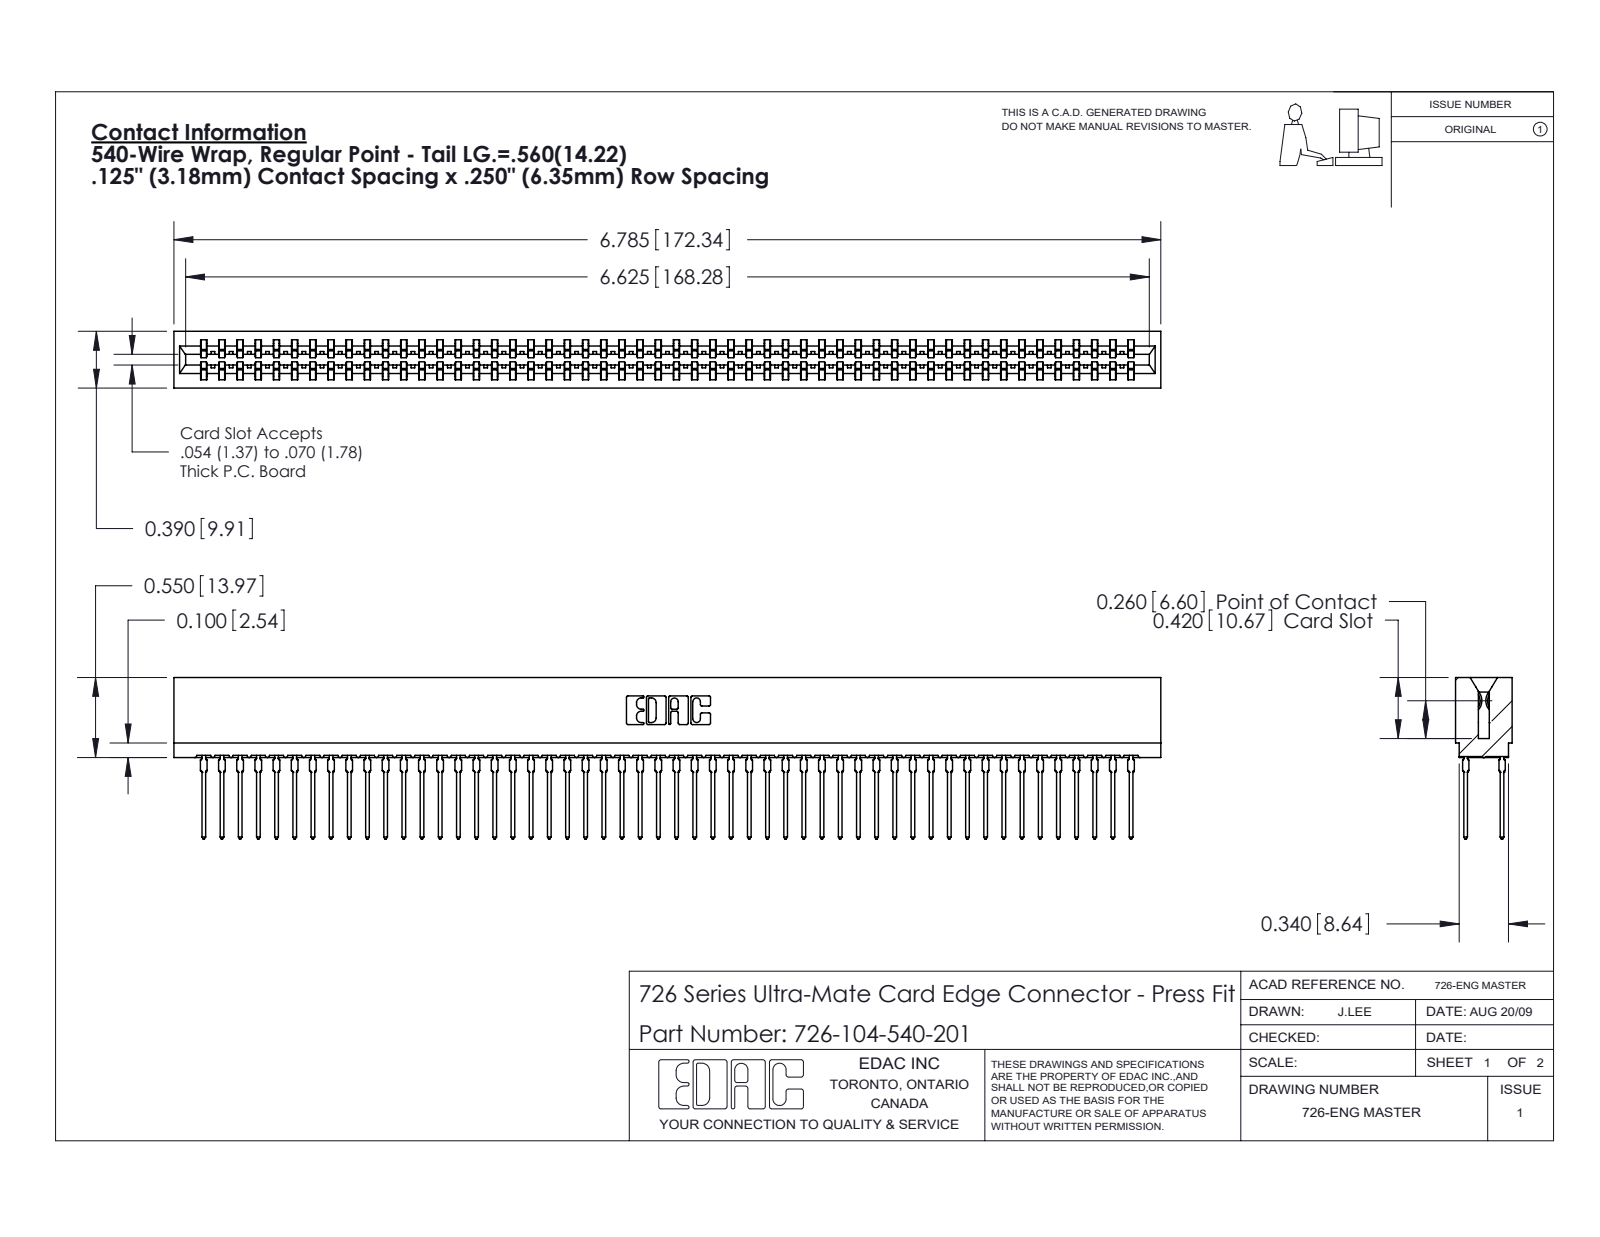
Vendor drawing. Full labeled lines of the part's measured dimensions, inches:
Part name (STEP PRODUCT): 726-104-540-201; 746-292-001_540; 726 Part_.515 Slot Depth - 01
STEP written by: SolidWorks 2020 (CONFIG_CONTROL_DESIGN)
Units: inches
Bodies: 105 solids, 9405 faces (4839 planar, 1862 cylindrical, 2704 other)
Overall size (bounding box): 6.785 × 1.109 × 0.39
Volume: 0.984 in³ · Surface area: 44.18 in²
Partial cylindrical surfaces — rounded edges, fillets, slot ends (radius × count): R0.021 ×208, R0.015 ×53, R0.01 ×22, R0.005 ×8, R0.011 ×8, R0.007 ×6, R0.031 ×6, R0.026 ×3
Main face-to-face distances: 0.057, 0.333, 0.025, 0.307, 0.25, 0.39, 0.275, 0.083, 0.365, 0.032
